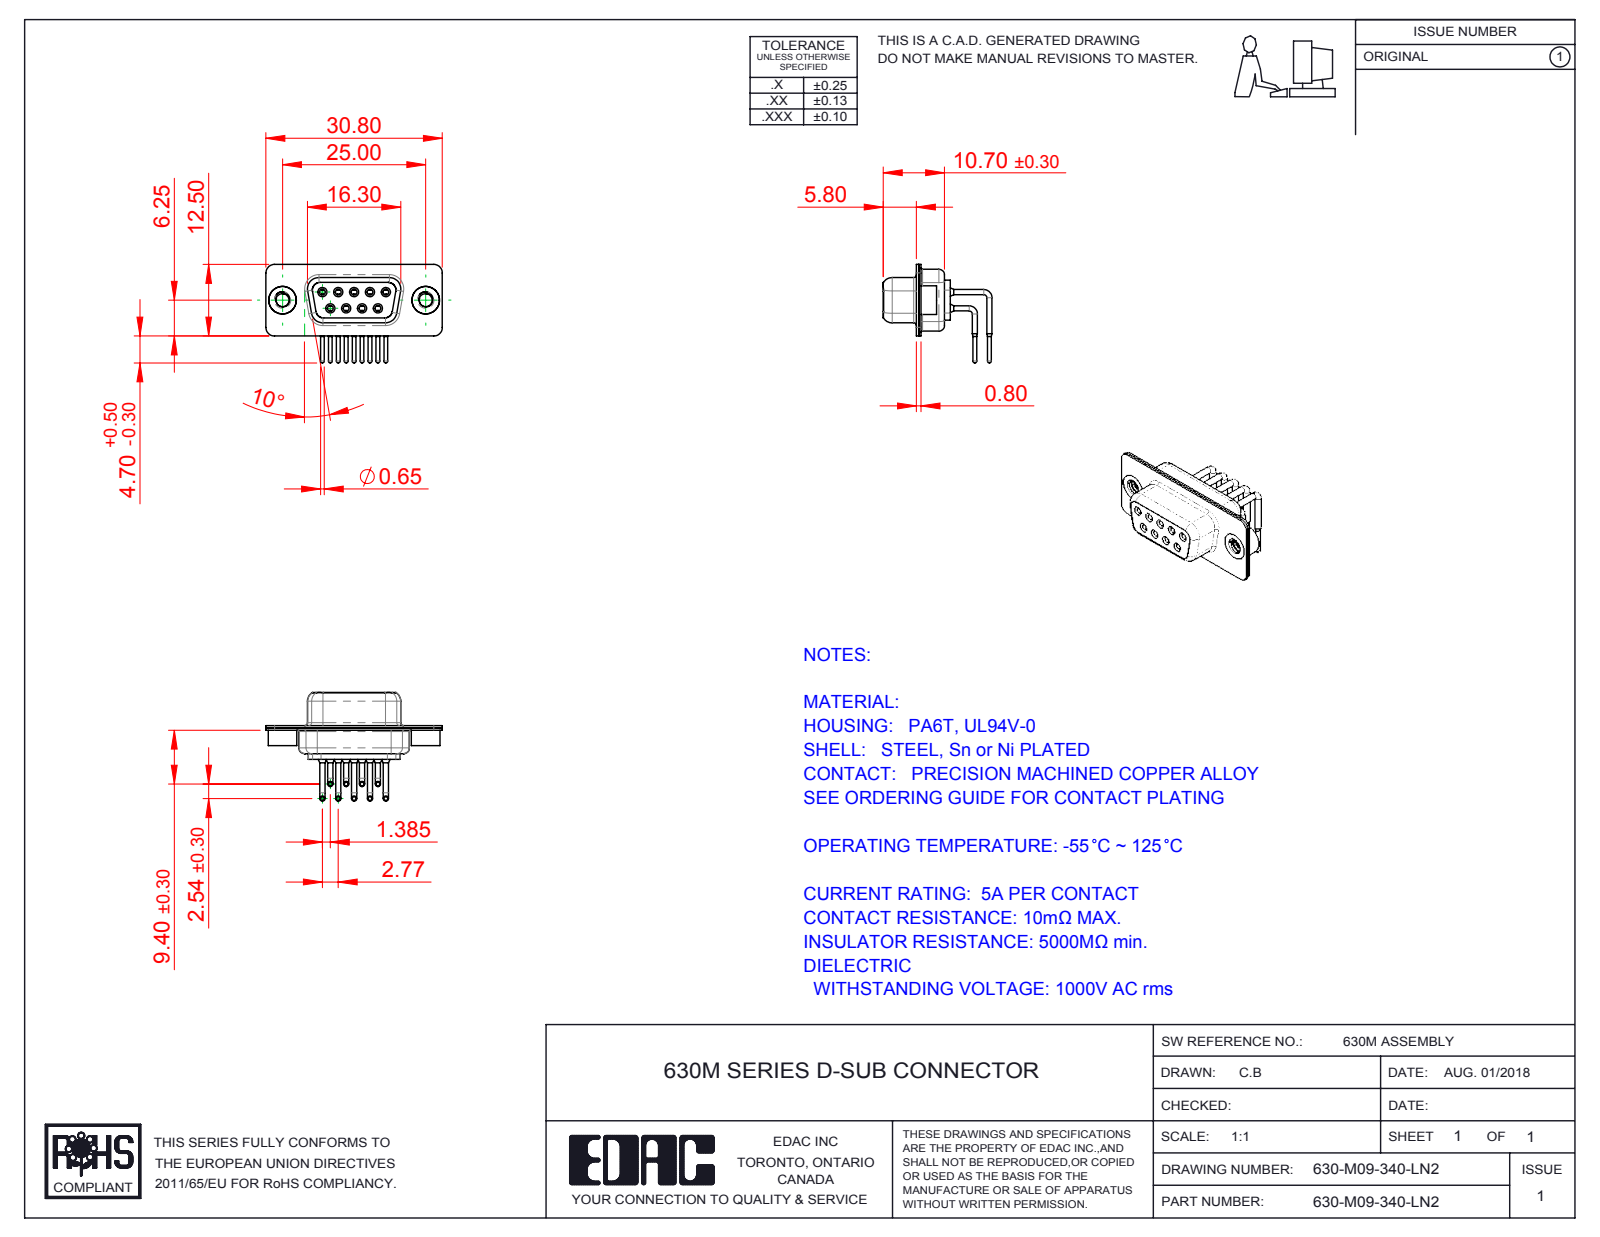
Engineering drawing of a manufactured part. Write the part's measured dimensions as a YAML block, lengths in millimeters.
part_name: "630-M09-340-LN2; 630M Housing_09 Contacts; 630M 4-40 Threaded Rivet; 630M Contact Row 2 (+3 more)"
step_written_by: "SolidWorks 2016 (CONFIG_CONTROL_DESIGN)"
units: millimeters
bodies: {solids: 14, faces: 756, planar: 202, cylindrical: 344, other: 210}
overall_size: [30.8, 18.99, 17.2]
volume: 1761
surface_area: 4640
round_holes:
  - {diameter: 1, count: 9}
  - {diameter: 1.1, count: 9}
  - {diameter: 1.7, count: 9}
  - {diameter: 1.8, count: 9}
  - {diameter: 2, count: 9}
  - {diameter: 2.26, count: 2}
  - {diameter: 4, count: 2}
  - {diameter: 4.8, count: 2}
round_bosses_or_shafts:
  - {diameter: 0.9, count: 18}
  - {diameter: 1.6, count: 9}
  - {diameter: 1.5, count: 9}
  - {diameter: 0.65, count: 9}
  - {diameter: 5, count: 2}
  - {diameter: 4.9, count: 2}
partial_cylinders:
  - {radius: 1.5, count: 16}
  - {radius: 2, count: 12}
  - {radius: 1.35, count: 8}
  - {radius: 1.6, count: 8}
  - {radius: 0.25, count: 4}
  - {radius: 0.5, count: 4}
  - {radius: 0.6, count: 4}
  - {radius: 0.65, count: 4}
face_to_face_distances: [0.4, 0.8, 1.45, 2.3, 8.95, 6.2, 8.5, 1.9, 0.85, 9.35]
hole_center_spacings: [3.16, 2.77, 5.54, 5.03, 5.04, 8.31, 7.1, 7.48]
